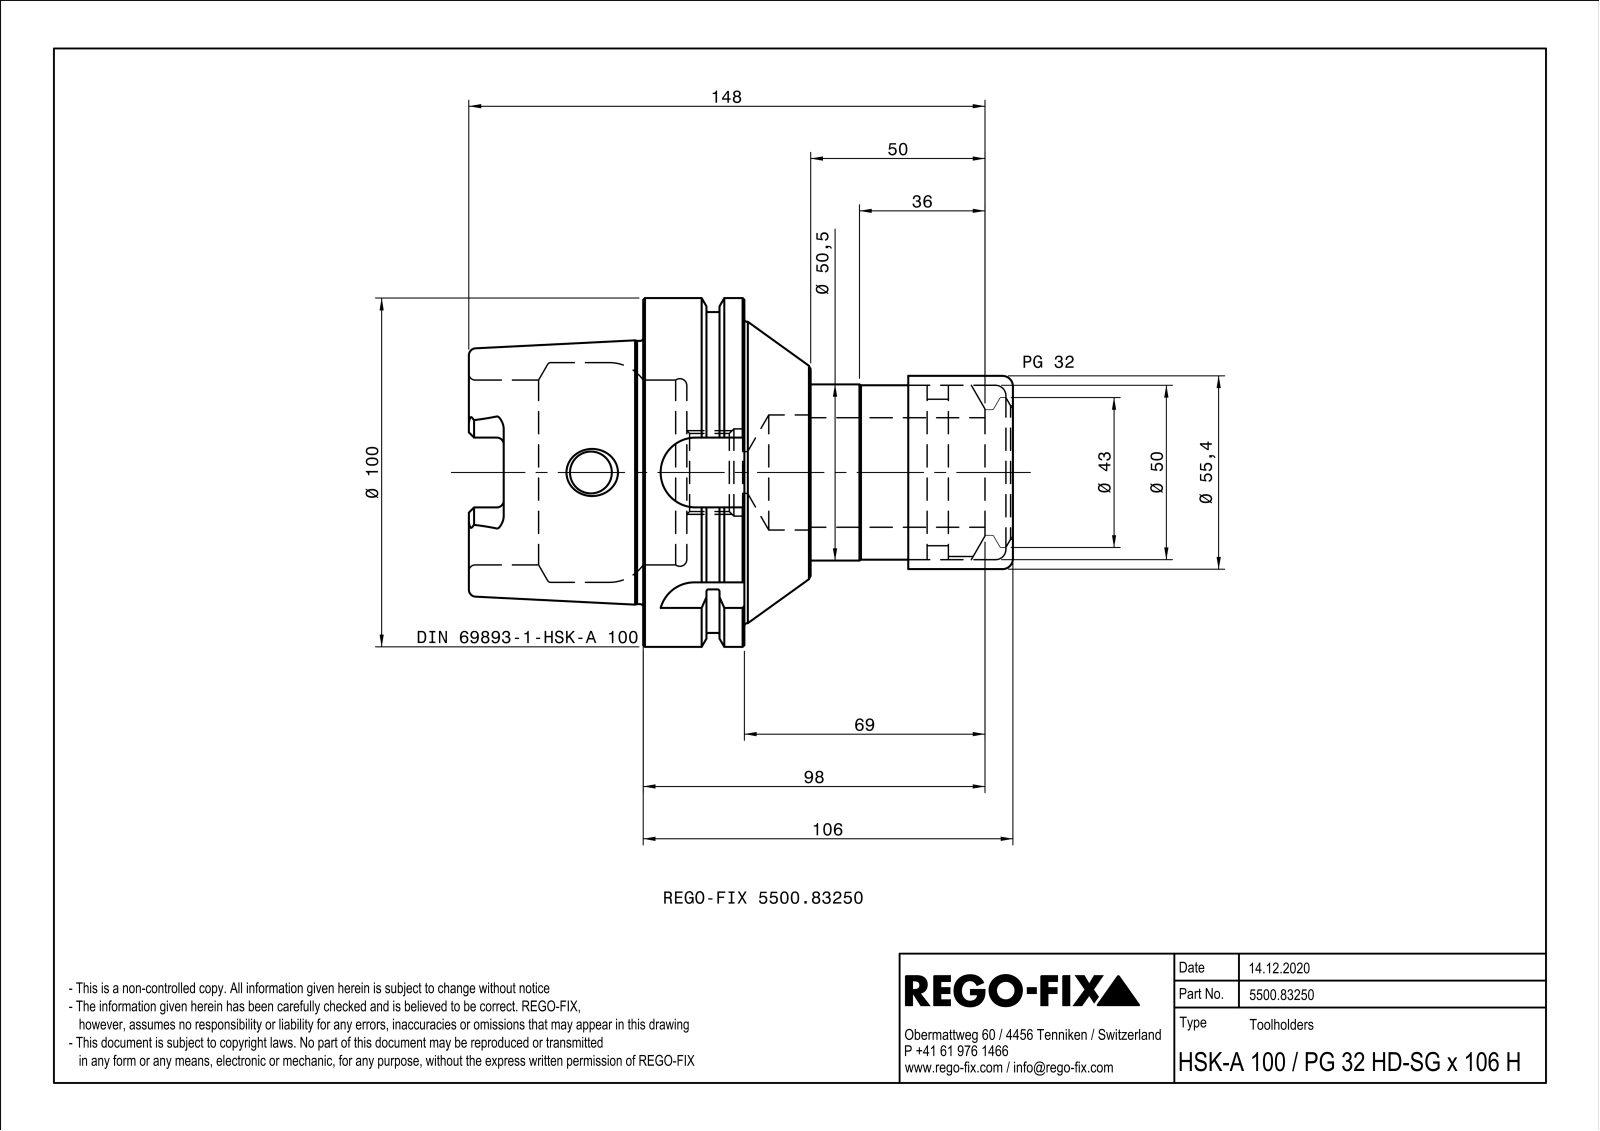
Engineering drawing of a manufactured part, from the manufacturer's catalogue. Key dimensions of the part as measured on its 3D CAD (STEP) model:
Part name (STEP PRODUCT): 0017497
STEP written by: SIEMENS PLM Software Solid Edge ST10 (AUTOMOTIVE_DESIGN)
Units: millimetres
Bodies: 2 solids, 155 faces (43 planar, 43 cylindrical, 69 other)
Overall size (bounding box): 156 × 100 × 100
Volume: 392 342 mm³ · Surface area: 78 245 mm²
Round holes (diameter × count): ⌀12 ×2, ⌀10 ×1, ⌀22.38 ×1, ⌀25 ×1, ⌀33 ×1, ⌀38.25 ×1, ⌀48.38 ×1, ⌀50.05 ×1, ⌀51 ×1, ⌀53 ×1, ⌀63 ×1
Round bosses / shafts (diameter × count): ⌀100 ×1, ⌀92 ×1, ⌀86.4 ×1, ⌀75.46 ×1, ⌀55.4 ×1, ⌀55 ×1, ⌀50.5 ×1, ⌀50 ×1
Partial cylindrical surfaces — rounded edges, fillets, slot ends (radius × count): R2 ×6, R4.88 ×4, R10 ×2, R11 ×1
Main face-to-face distances: 16.5, 12.5, 29, 50, 98, 79, 62.5, 77, 93.5, 106
